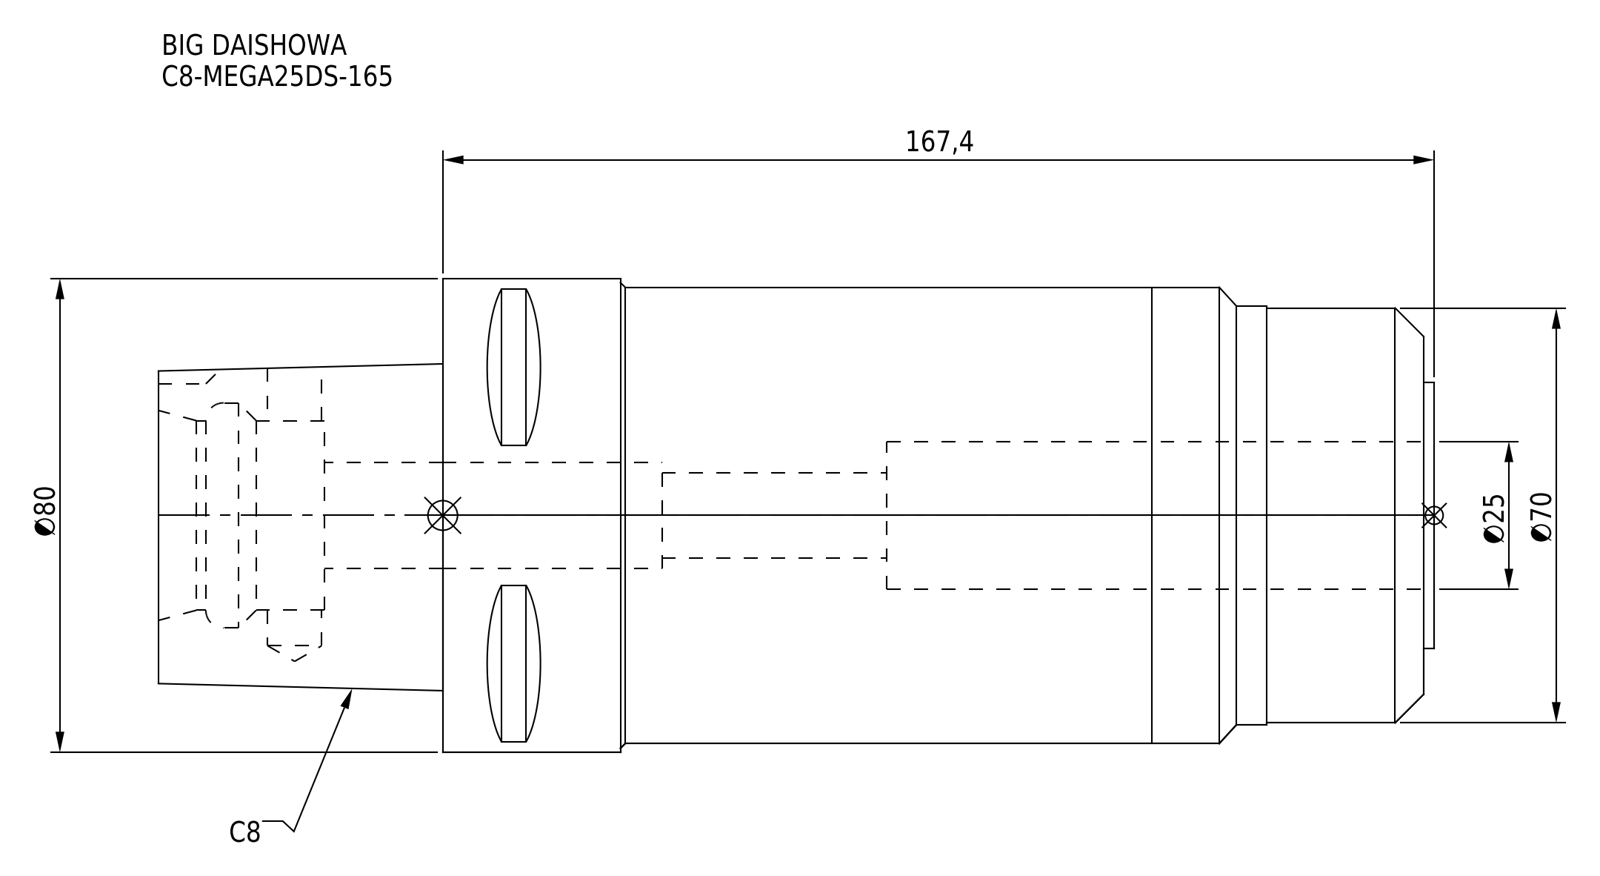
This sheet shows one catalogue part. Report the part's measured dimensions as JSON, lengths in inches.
{"part_name": "C8-MEGA25DS-165", "step_written_by": "CREO PARAMETRIC BY PTC INC, 2016380 (AUTOMOTIVE_DESIGN)", "units": "inches", "bodies": {"solids": 1, "faces": 74, "planar": 31, "cylindrical": 27, "other": 16}, "overall_size": [8.48, 3.15, 3.15], "volume_in3": 46.97, "surface_area_in2": 112.5, "round_holes": [[0.358, 1], [0.571, 1], [0.709, 1], [0.984, 1], [1.26, 1], [1.496, 1]], "round_bosses_or_shafts": [[3.15, 1], [3.031, 1], [2.783, 1], [2.756, 1], [1.764, 1]], "partial_cylinders_radius": [[0.236, 1]], "face_to_face_distances": [6.52, 0.071, 6.591, 8.48, 8.409, 1.89, 0.787, 7.378, 7.307, 1.102]}
